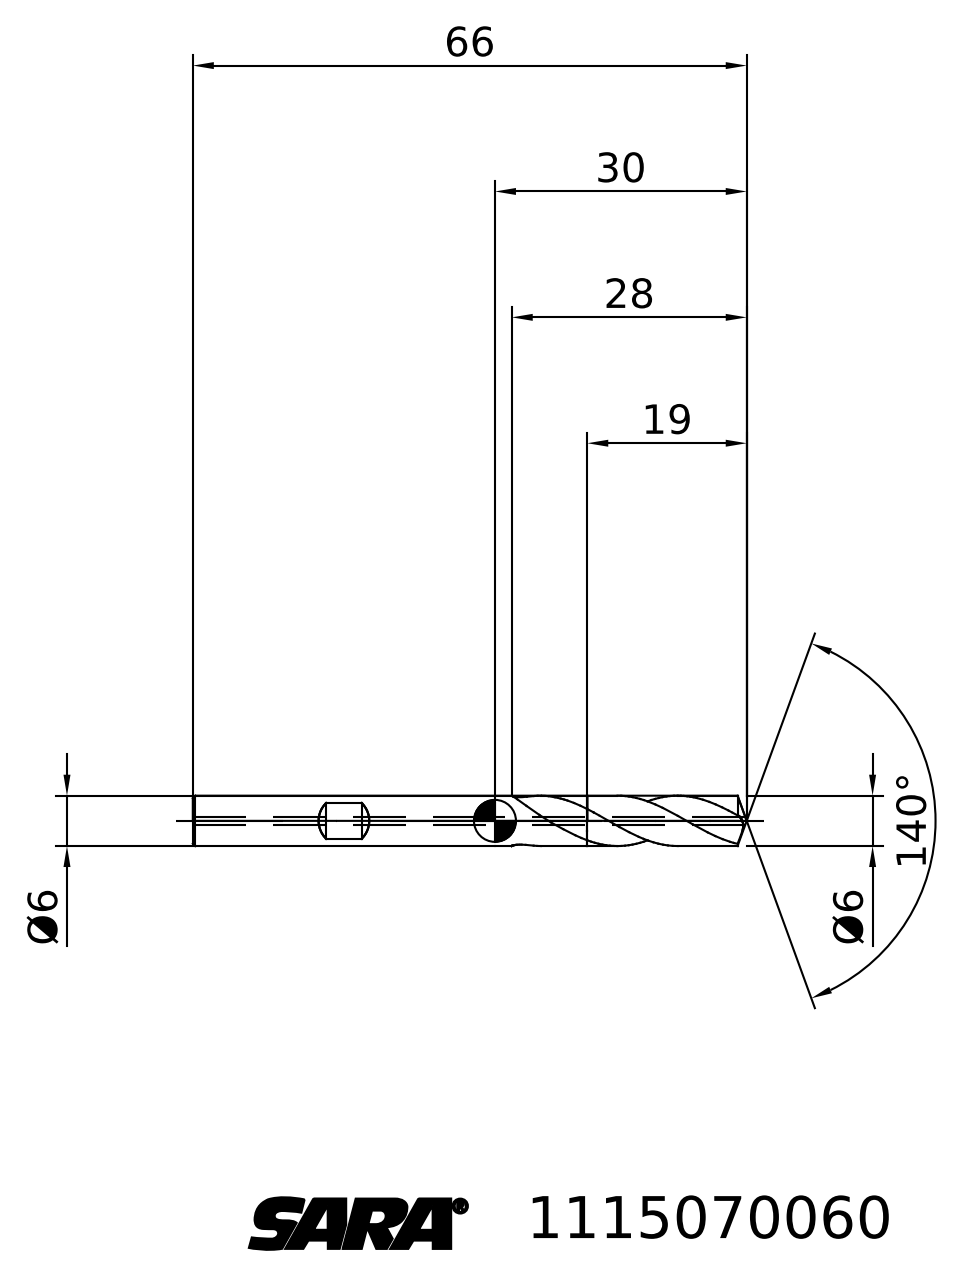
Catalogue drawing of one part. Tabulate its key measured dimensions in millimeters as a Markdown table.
| quantity | value |
| --- | --- |
| STEP written by | TDM (AUTOMOTIVE_DESIGN) |
| units | millimeters |
| bodies | 2 solids, 28 faces (6 planar, 0 cylindrical, 22 other) |
| overall size | 66 × 9.4 × 6 |
| volume | 1 585 mm³ |
| surface area | 1 353 mm² |
| main face-to-face distances | 47 |
